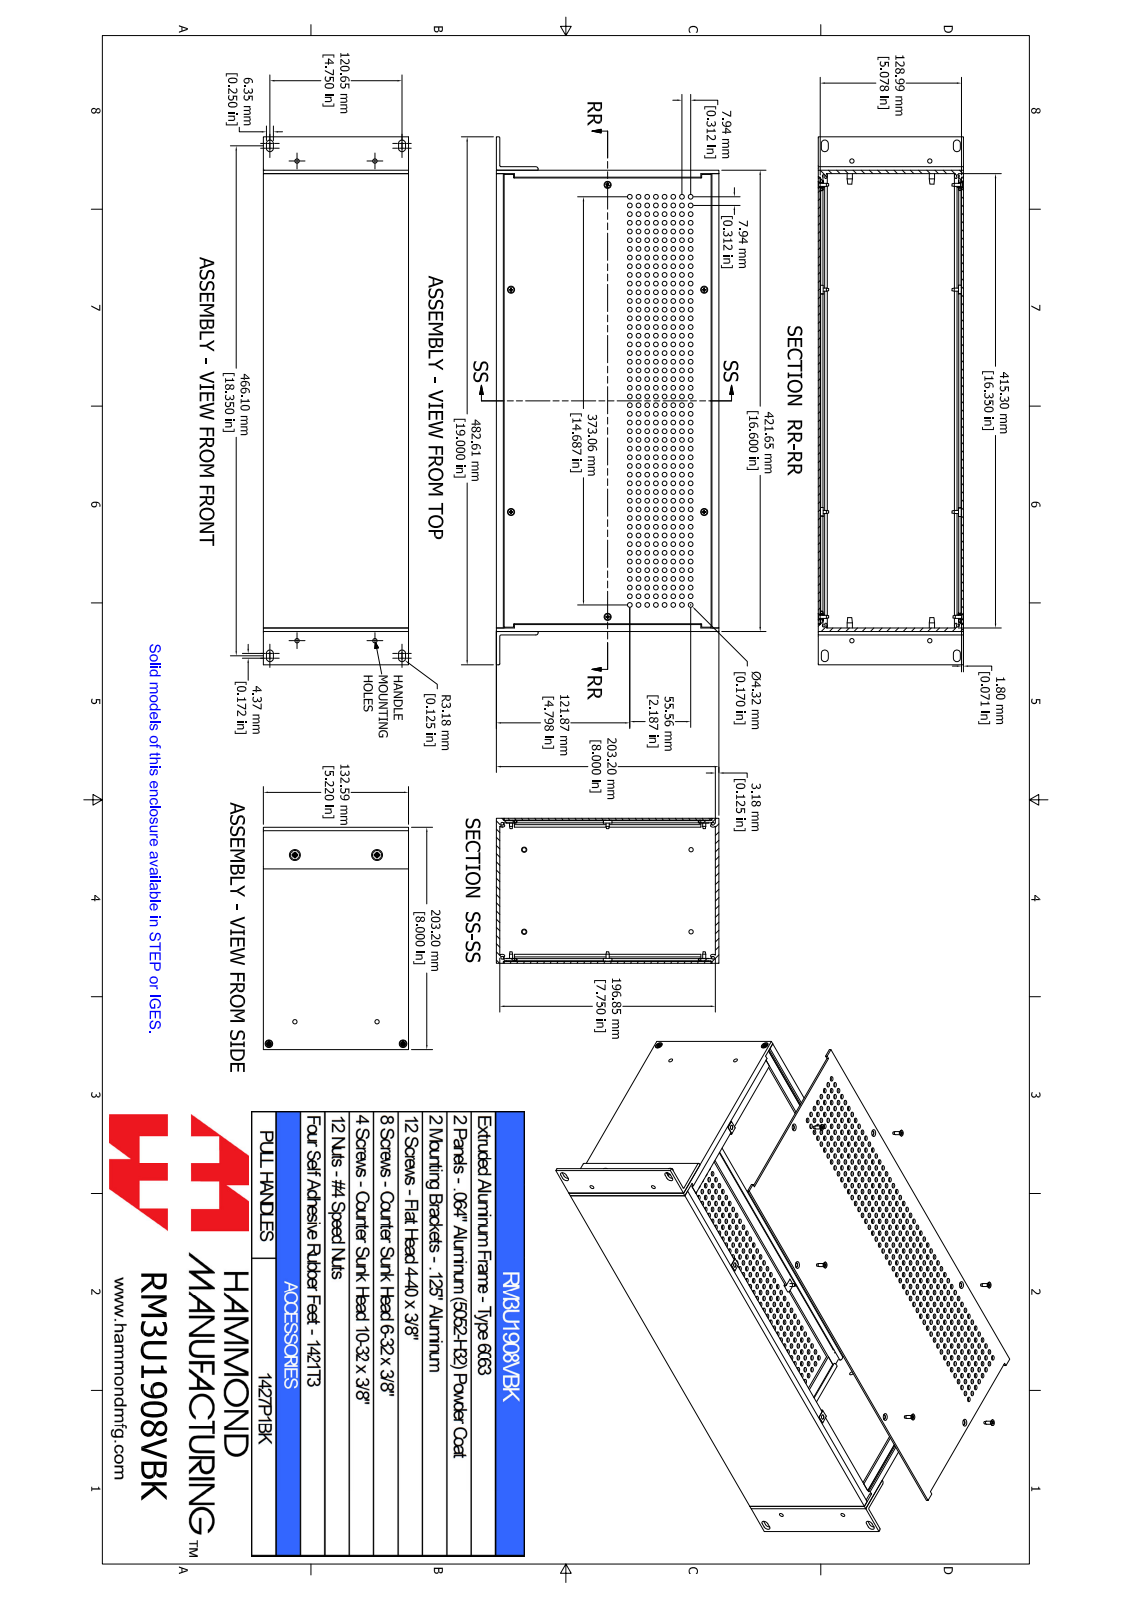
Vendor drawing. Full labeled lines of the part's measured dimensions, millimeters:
Part name (STEP PRODUCT): RM3U1908VBK
STEP written by: SolidWorks 2021 (AUTOMOTIVE_DESIGN)
Units: millimetres
Bodies: 44 solids, 1952 faces (564 planar, 956 cylindrical, 432 other)
Overall size (bounding box): 482.6 × 203.2 × 132.6
Volume: 936 700 mm³ · Surface area: 773 500 mm²
Round holes (diameter × count): ⌀4.3 ×384, ⌀2.5 ×6, ⌀4 ×6, ⌀4.3 ×6, ⌀3.5 ×4, ⌀4 ×4, ⌀4 ×4, ⌀5 ×2
Round bosses / shafts (diameter × count): ⌀5.4 ×6, ⌀2.8 ×6, ⌀6 ×4, ⌀3.5 ×4, ⌀8.5 ×2, ⌀4.8 ×2
Partial cylindrical surfaces — rounded edges, fillets, slot ends (radius × count): R1 ×18, R3.2 ×16, R1.2 ×12, R0.9 ×8, R1.3 ×8, R1 ×4, R2 ×2
Main face-to-face distances: 1.8, 130.8, 3.2, 3.2, 132.6, 129, 203.2, 200, 196.9, 200
Hole centre spacings: 17.8, 8, 15.9, 25.1, 32.7, 7.9, 11.2, 17.7
